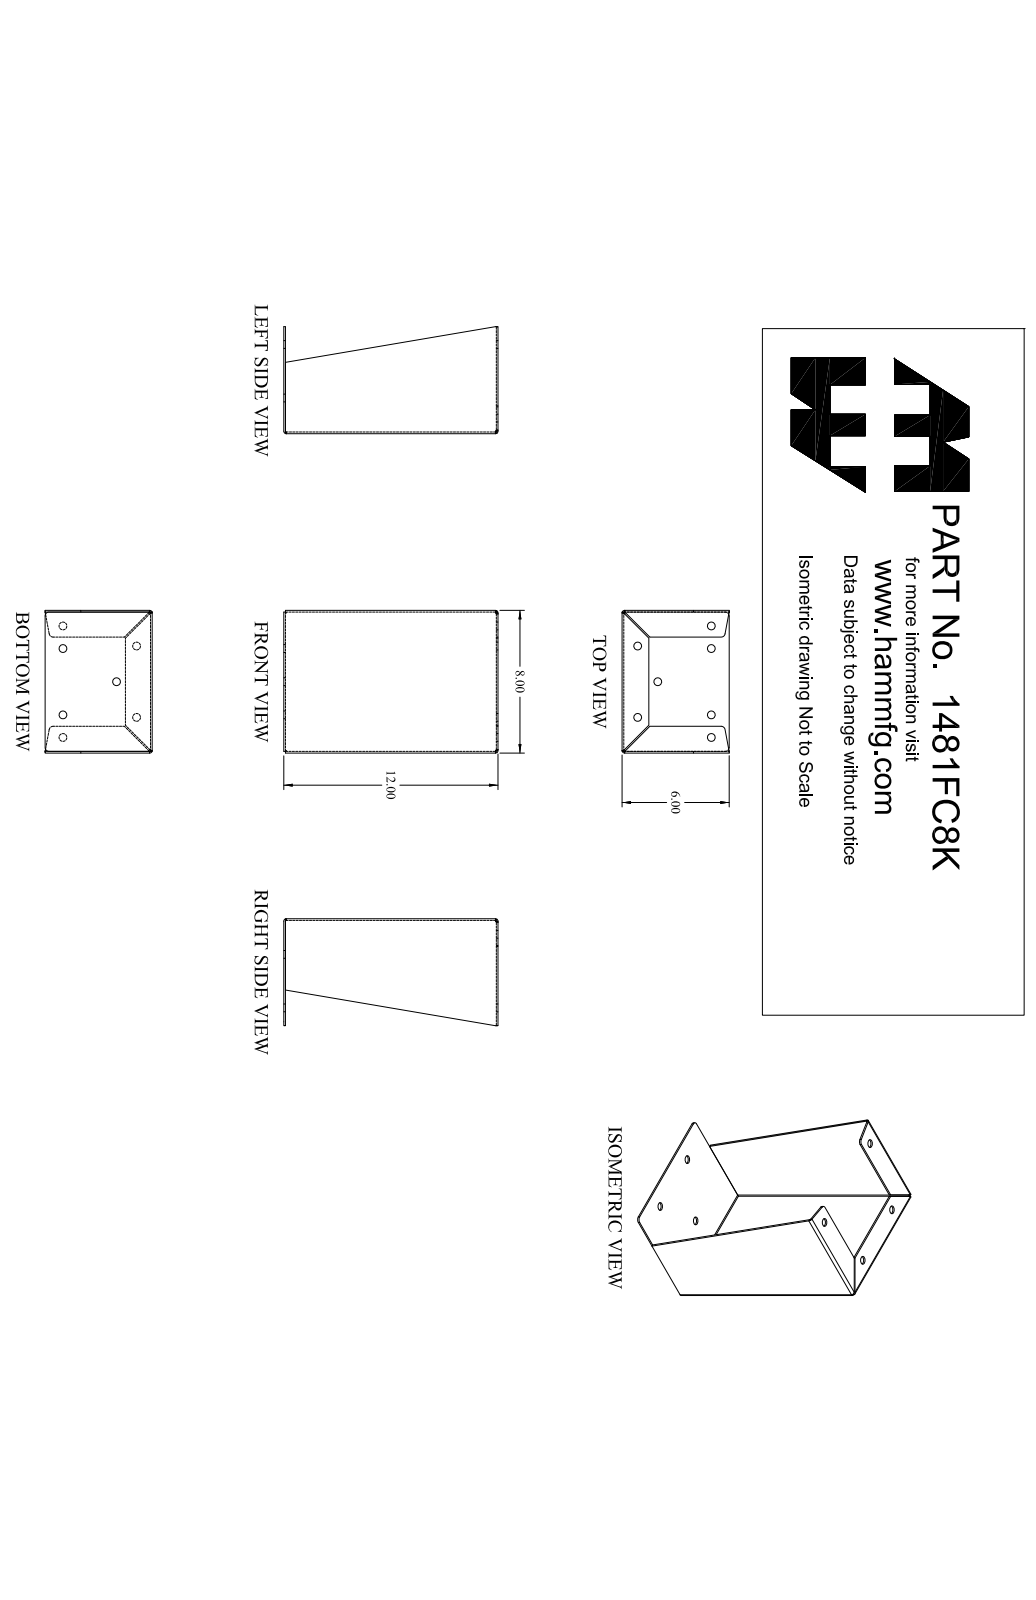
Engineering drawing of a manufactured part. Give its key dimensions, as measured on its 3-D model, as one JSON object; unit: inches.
{"part_name": "1481FC8K_Default", "step_written_by": "SolidWorks 2019 (CONFIG_CONTROL_DESIGN)", "units": "inches", "bodies": {"solids": 1, "faces": 78, "planar": 42, "cylindrical": 30, "other": 6}, "overall_size": [12, 8, 6], "volume_in3": 26.49, "surface_area_in2": 565.9, "round_holes": [[0.437, 7]], "partial_cylinders_radius": [[0.048, 6], [0.143, 6], [0.22, 4]], "face_to_face_distances": [0.095, 7.905, 8, 7.81, 0.095, 11.81, 11.905, 11.905, 12, 1.405], "hole_center_spacings": [1.266, 2.294, 3.529, 4.127, 4.276, 4.332, 4.984, 5.648]}
